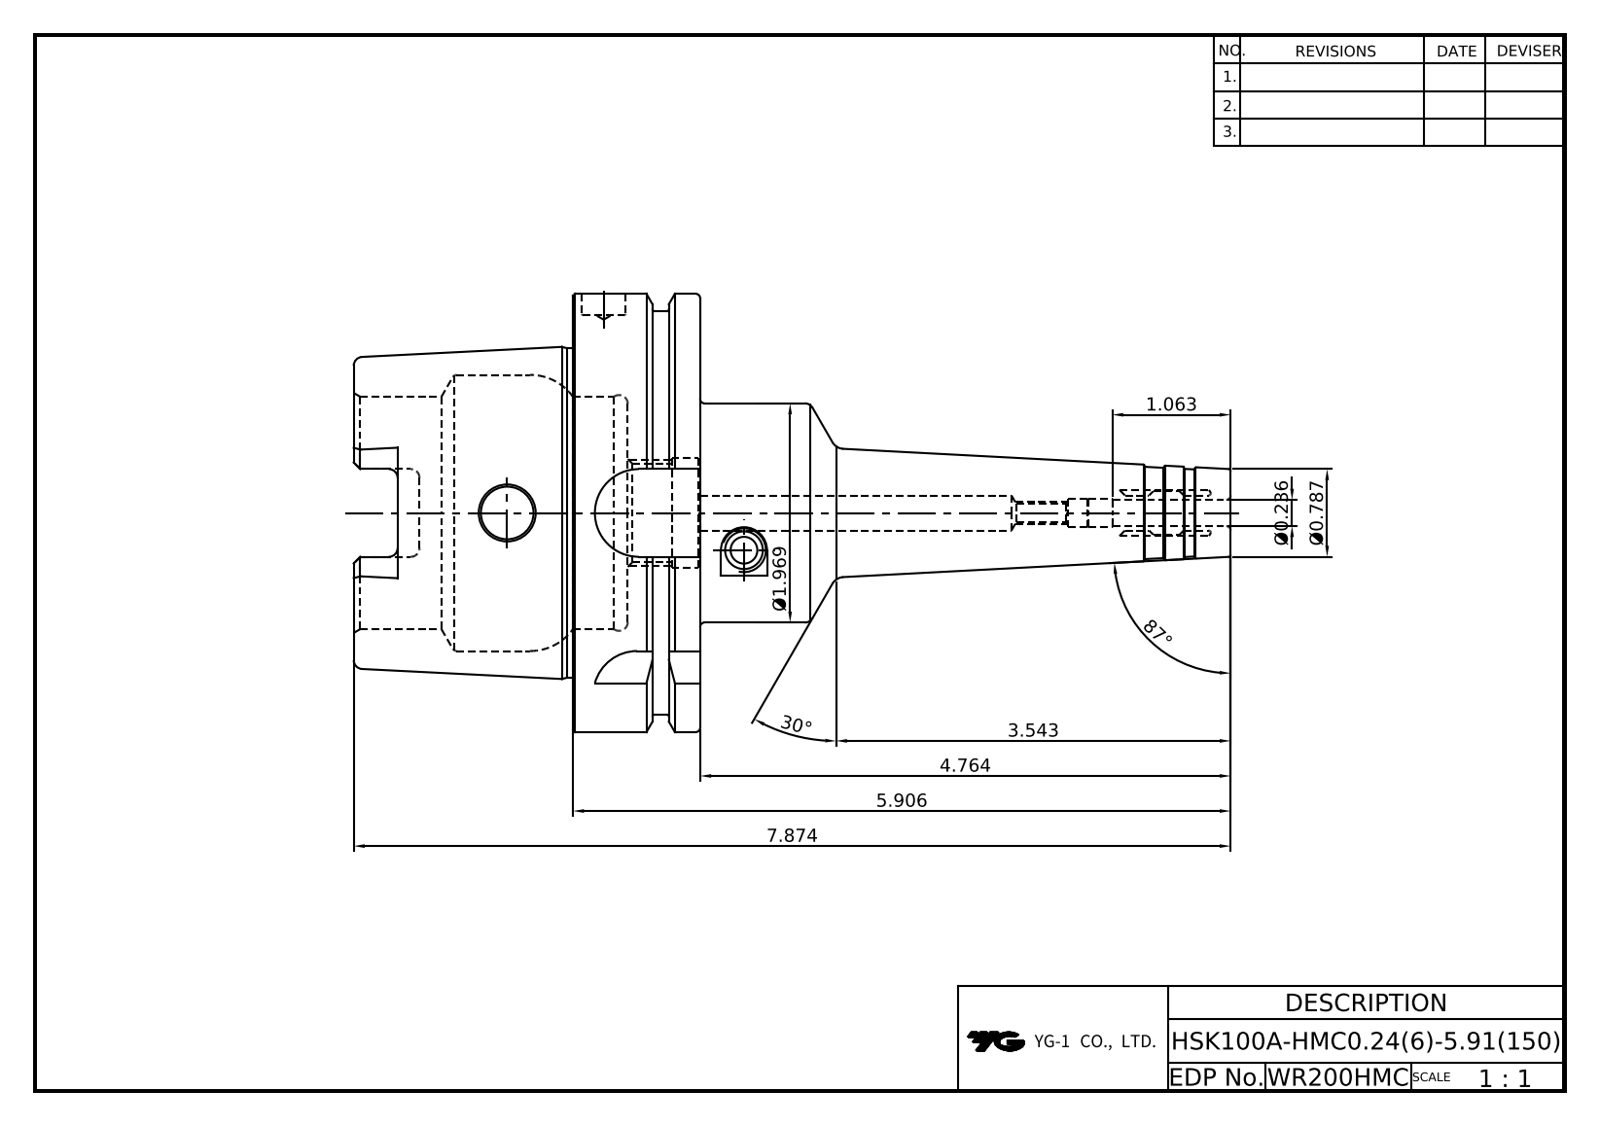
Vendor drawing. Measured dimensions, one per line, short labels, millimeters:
name: HSK100A-HMC6-150
written by: Autodesk Inventor 2020 (AUTOMOTIVE_DESIGN)
unit: mm
bodies: 1 solid, 134 faces (38 planar, 35 cylindrical, 61 other)
size: 200 × 100 × 100
volume: 337 361 mm³; area: 62 369 mm²
holes: 1× ⌀4.3, 1× ⌀6, 1× ⌀6.6, 1× ⌀8, 1× ⌀10, 1× ⌀12, 1× ⌀22.38, 1× ⌀25, 1× ⌀53, 1× ⌀63
bosses: 1× ⌀100, 1× ⌀92, 1× ⌀75.41, 1× ⌀50
rounds: 6× R2, 4× R4.88, 4× R10
face distances: 29, 12.5, 16.5, 62.5, 50, 79, 88, 78.5, 28.5, 16
